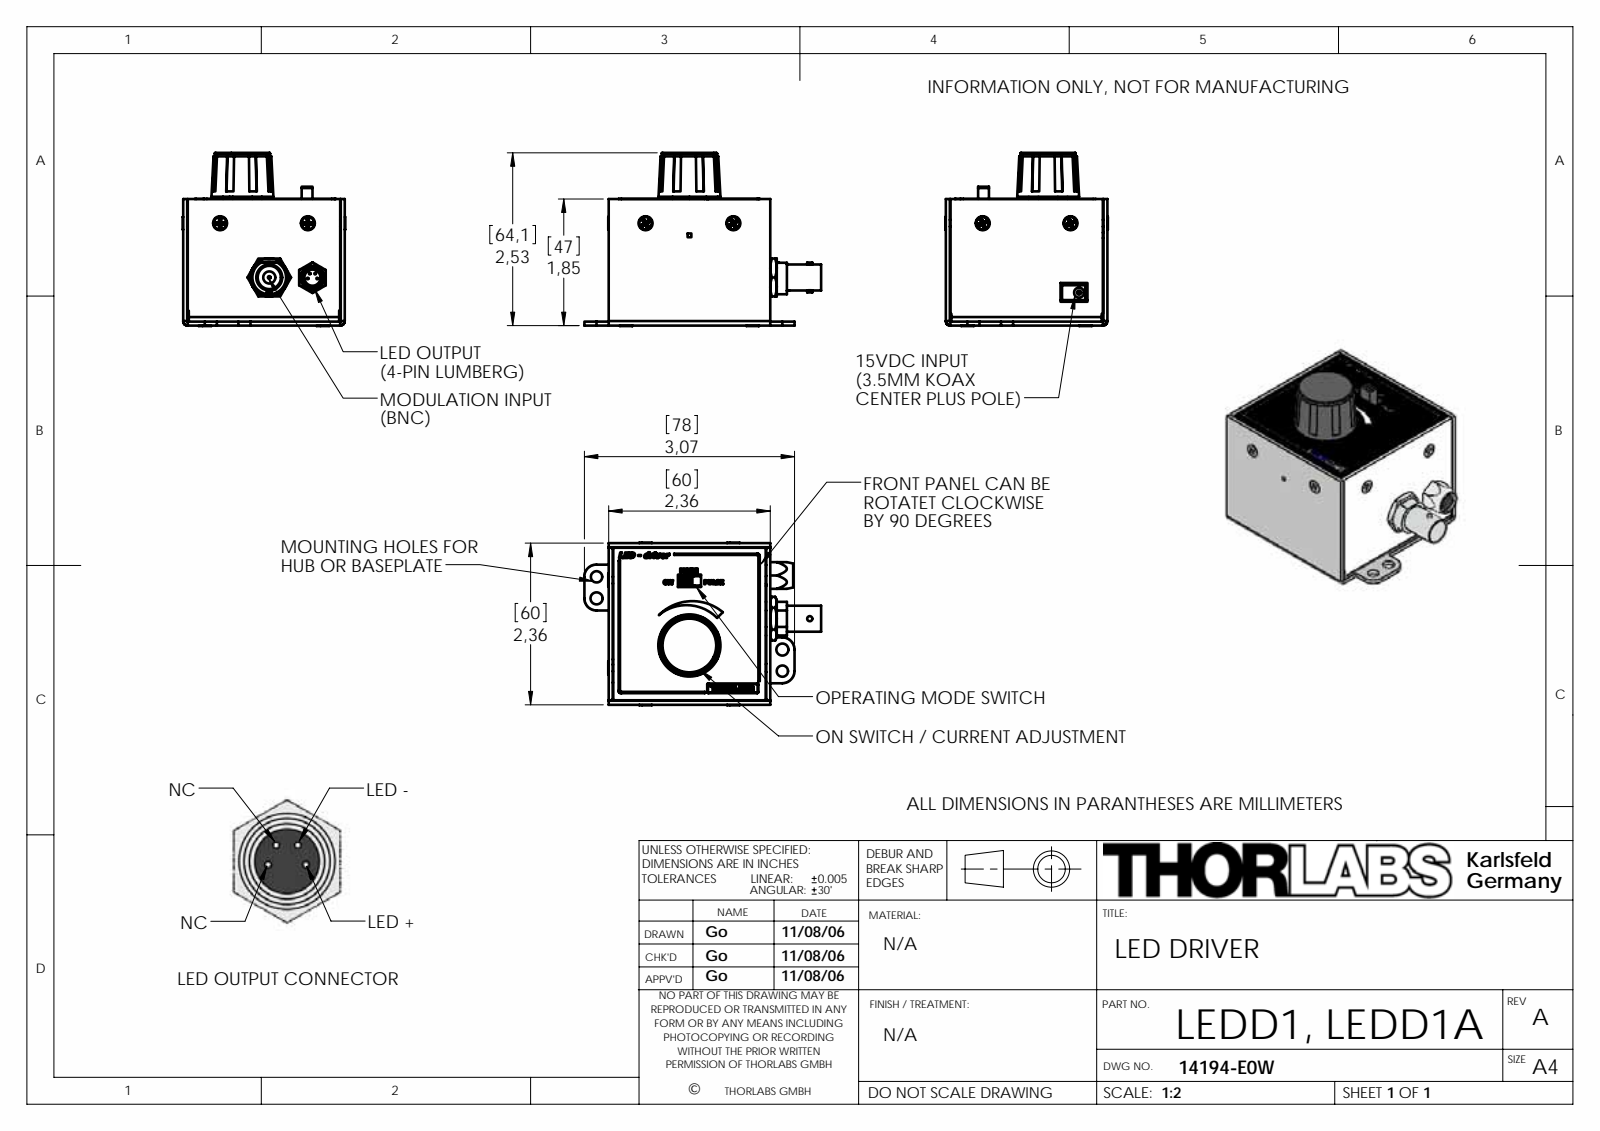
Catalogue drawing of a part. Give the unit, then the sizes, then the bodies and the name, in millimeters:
Units: millimetres
Overall size (bounding box): 87.86 × 64.3 × 60.3
Round holes (diameter × count): ⌀0.6 ×4, ⌀4.2 ×2, ⌀4.5 ×2, ⌀3.7 ×1, ⌀7 ×1, ⌀8 ×1, ⌀8.64 ×1
Round bosses / shafts (diameter × count): ⌀4.7 ×8, ⌀20.5 ×1, ⌀12.5 ×1, ⌀9.65 ×1, ⌀6 ×1, ⌀1.91 ×1, ⌀1.9 ×1
Partial cylindrical surfaces — rounded edges, fillets, slot ends (radius × count): R1.7 ×4, R4.5 ×4, R0.2 ×3, R1 ×1, R16.08 ×1, R17.57 ×1
Main face-to-face distances: 1.5, 58.5, 60, 57, 1.51, 6.49, 8, 47, 39, 45.49
Hole centre spacings: 1.78, 1.8, 1.95, 3.29, 8, 74.09, 2, 3.5
Bodies: 0 solids, 709 faces (570 planar, 71 cylindrical, 68 other)
Part name (STEP PRODUCT): 14194-E0w
STEP written by: SolidWorks 2007 (AUTOMOTIVE_DESIGN)
